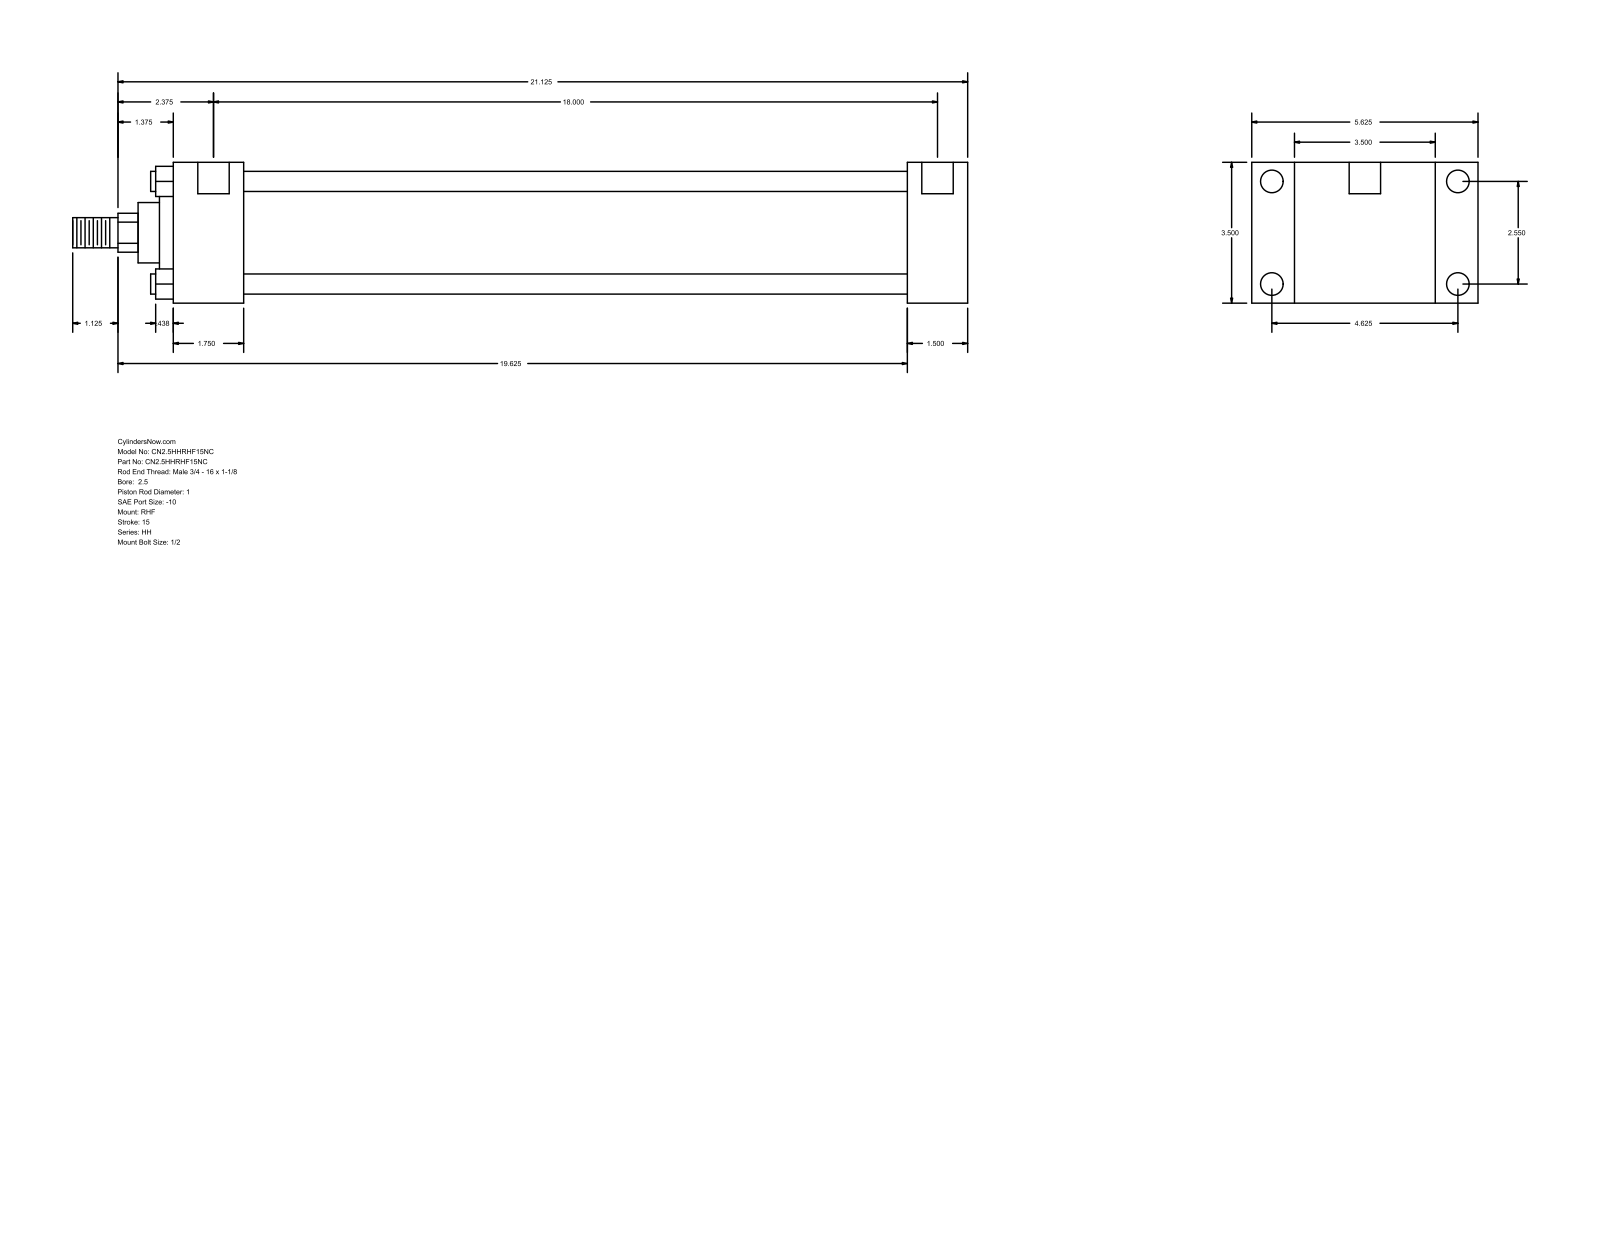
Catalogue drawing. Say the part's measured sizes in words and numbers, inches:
The part is named "HH_RHF__0250_1". Its 3-D file was written by "GSSL Pune (CONFIG_CONTROL_DESIGN)". It is 0 solids with 90 faces: 61 planar, 29 cylindrical and 0 other. Overall it measures 22.25 by 5.625 by 3.5 inches. Round holes: 4 of diameter 0.219, 4 of diameter 0.563, 2 of diameter 0.781. Round bosses or shafts: 4 of diameter 0.5, 1 of diameter 2.875, 1 of diameter 2.375, 1 of diameter 1.5, 1 of diameter 1, 1 of diameter 0.75. Partial cylindrical surfaces (rounded edges, fillets, slot ends): 1 of radius 0.484. The main face-to-face distances are 3.5, 1.5, 1.063, 4.563, 18.25, 19.75, 5.625, 1.75, 16.5, 18. The hole center spacings are 0.063, 2.55, 4.625, 5.281, 18.062, 18.125, 18.
